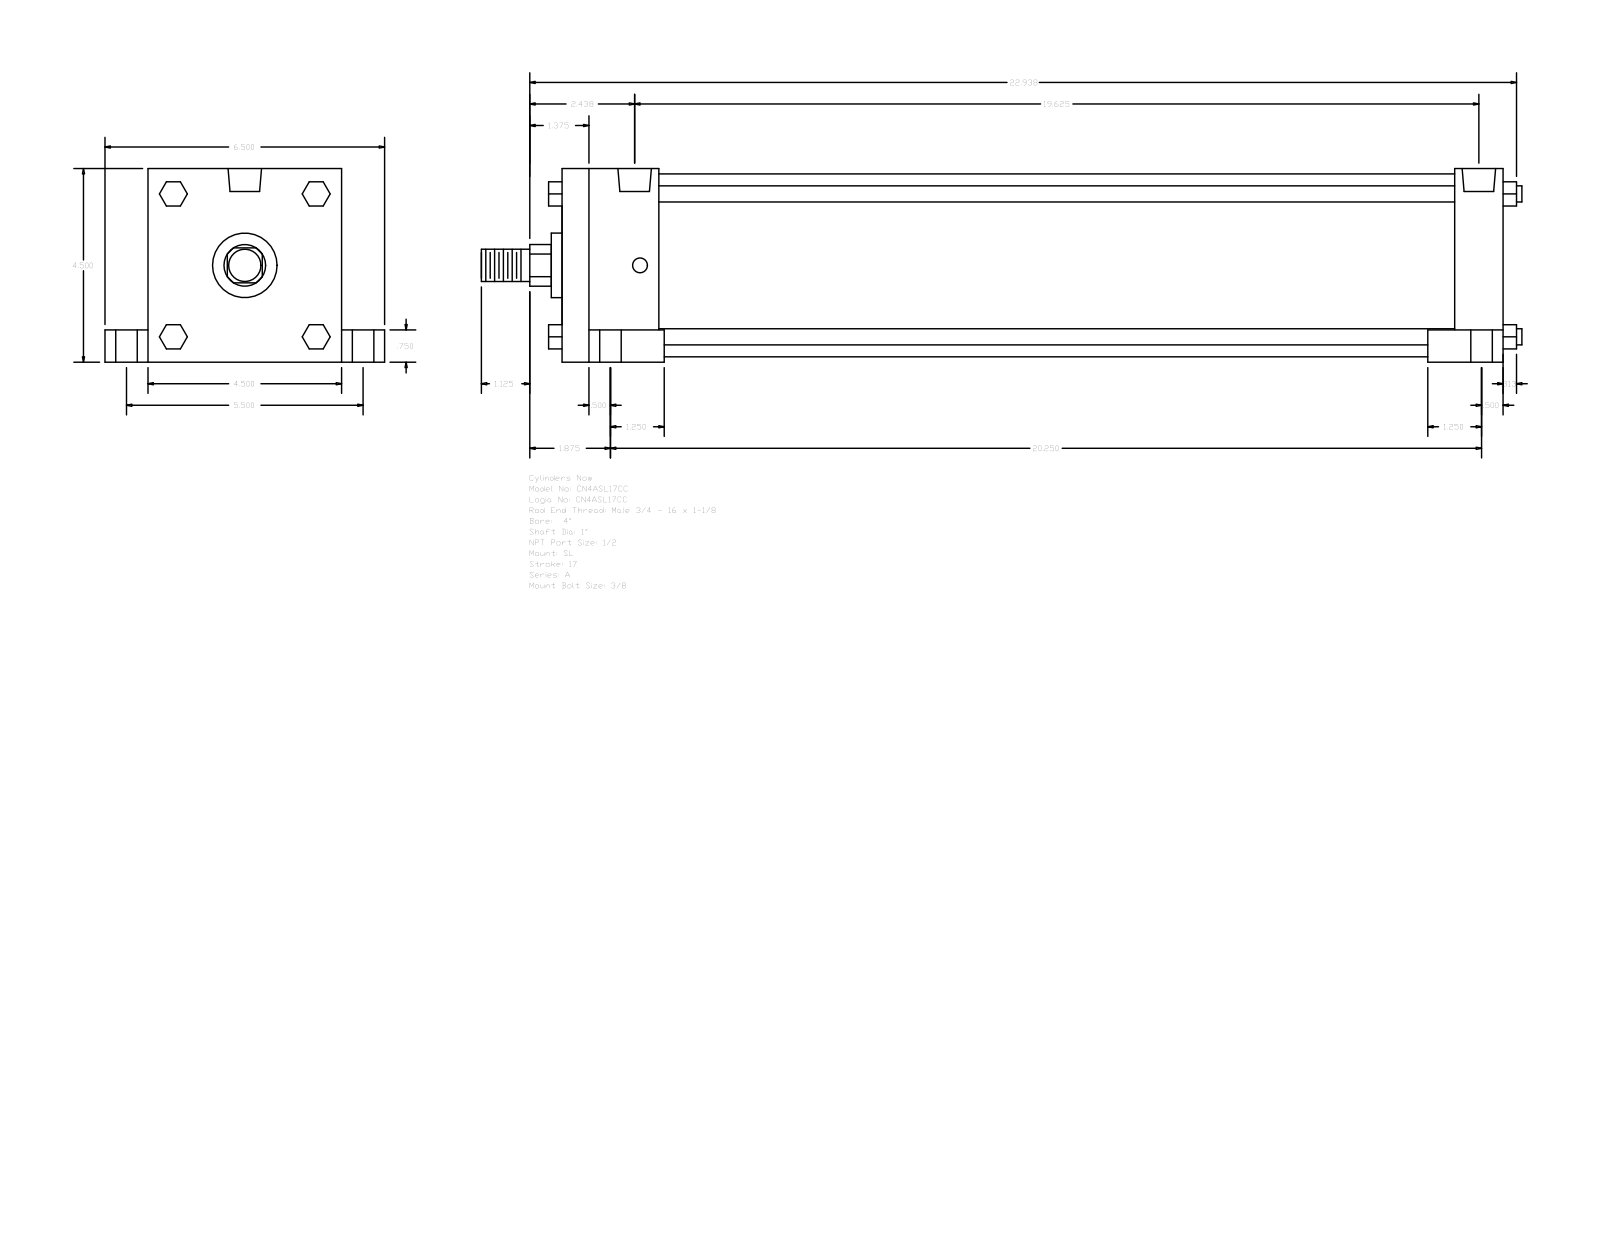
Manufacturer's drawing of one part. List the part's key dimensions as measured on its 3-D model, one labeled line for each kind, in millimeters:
Part name (STEP PRODUCT): A_SL__0400_1
STEP written by: GSSL Pune (CONFIG_CONTROL_DESIGN)
Units: millimetres
Bodies: 0 solids, 150 faces (114 planar, 36 cylindrical, 0 other)
Overall size (bounding box): 614.36 × 165.1 × 114.3
Round holes (diameter × count): ⌀8.73 ×4, ⌀12.7 ×4, ⌀19.05 ×4, ⌀19.77 ×2
Round bosses / shafts (diameter × count): ⌀9.53 ×4, ⌀107.95 ×1, ⌀38.1 ×1, ⌀25.4 ×1, ⌀19.05 ×1
Partial cylindrical surfaces — rounded edges, fillets, slot ends (radius × count): R12.29 ×1
Main face-to-face distances: 114.3, 555.62, 28.57, 57.15, 498.47, 527.05, 469.9, 19.05, 25.4, 139.7
Hole centre spacings: 3.18, 69.87, 70.01, 71.3, 72, 139.7, 492.12, 495.3
